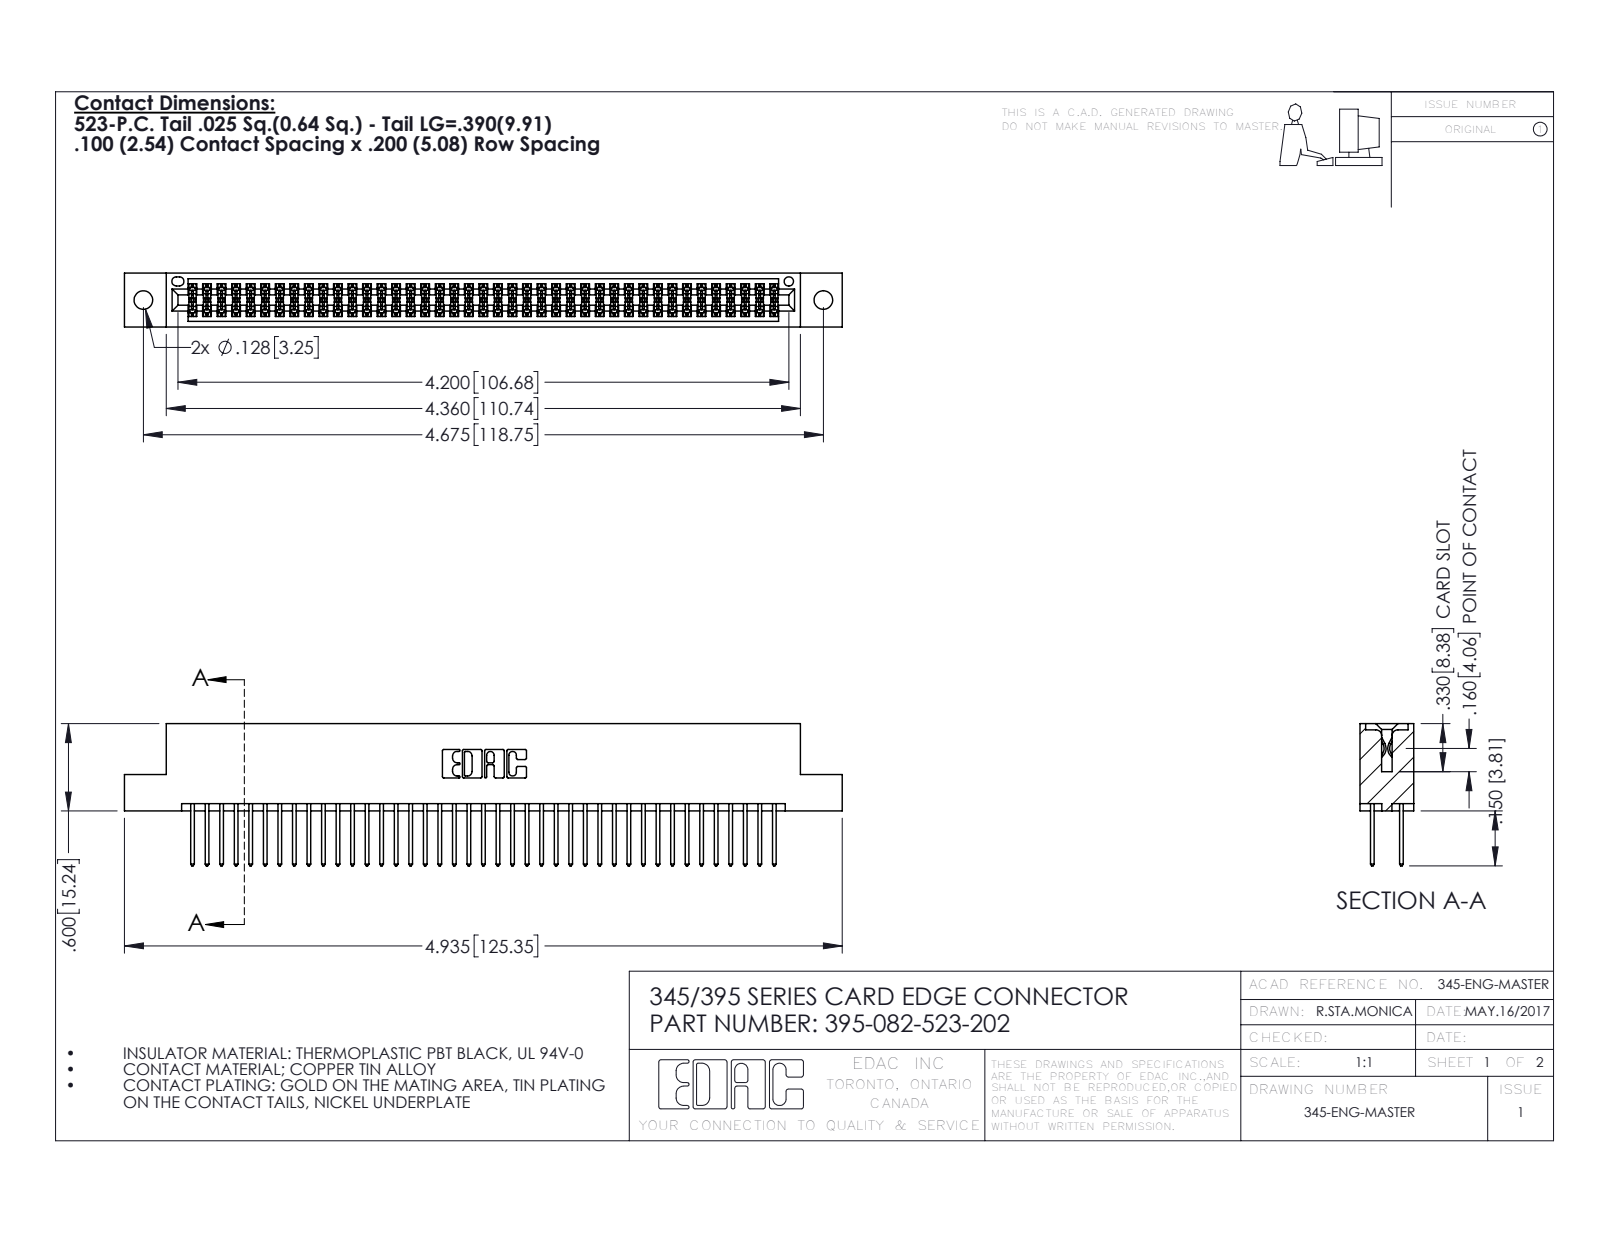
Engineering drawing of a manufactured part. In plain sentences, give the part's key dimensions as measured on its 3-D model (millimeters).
The part is named "345-292-001_345-293-123; 395-082-523-202; 345 Part_Flush Mounting Lugs - 0.128 Dia". Its 3-D file was written by "SolidWorks 2016 (CONFIG_CONTROL_DESIGN)". It is 83 solids with 4226 faces: 2786 planar, 1440 cylindrical and 0 other. Overall it measures 125.3 by 24.8 by 9.4 millimeters. Its volume is 12 300 cubic millimeters and its surface area 18 640 square millimeters. Round holes: 2 of diameter 3.3, 1 of diameter 1.6. Partial cylindrical surfaces (rounded edges, fillets, slot ends): 123 of radius 0.2, 82 of radius 0.3, 22 of radius 0.3, 6 of radius 0.2, 6 of radius 0.8, 3 of radius 0.7, 2 of radius 0.4, 2 of radius 0.5. The main face-to-face distances are 7.6, 1.8, 5.1, 2.5, 6.9, 0.6, 9.4, 5.7, 4.4, 3.8. The hole center spacings are 6.9, 112.8, 118.7.
